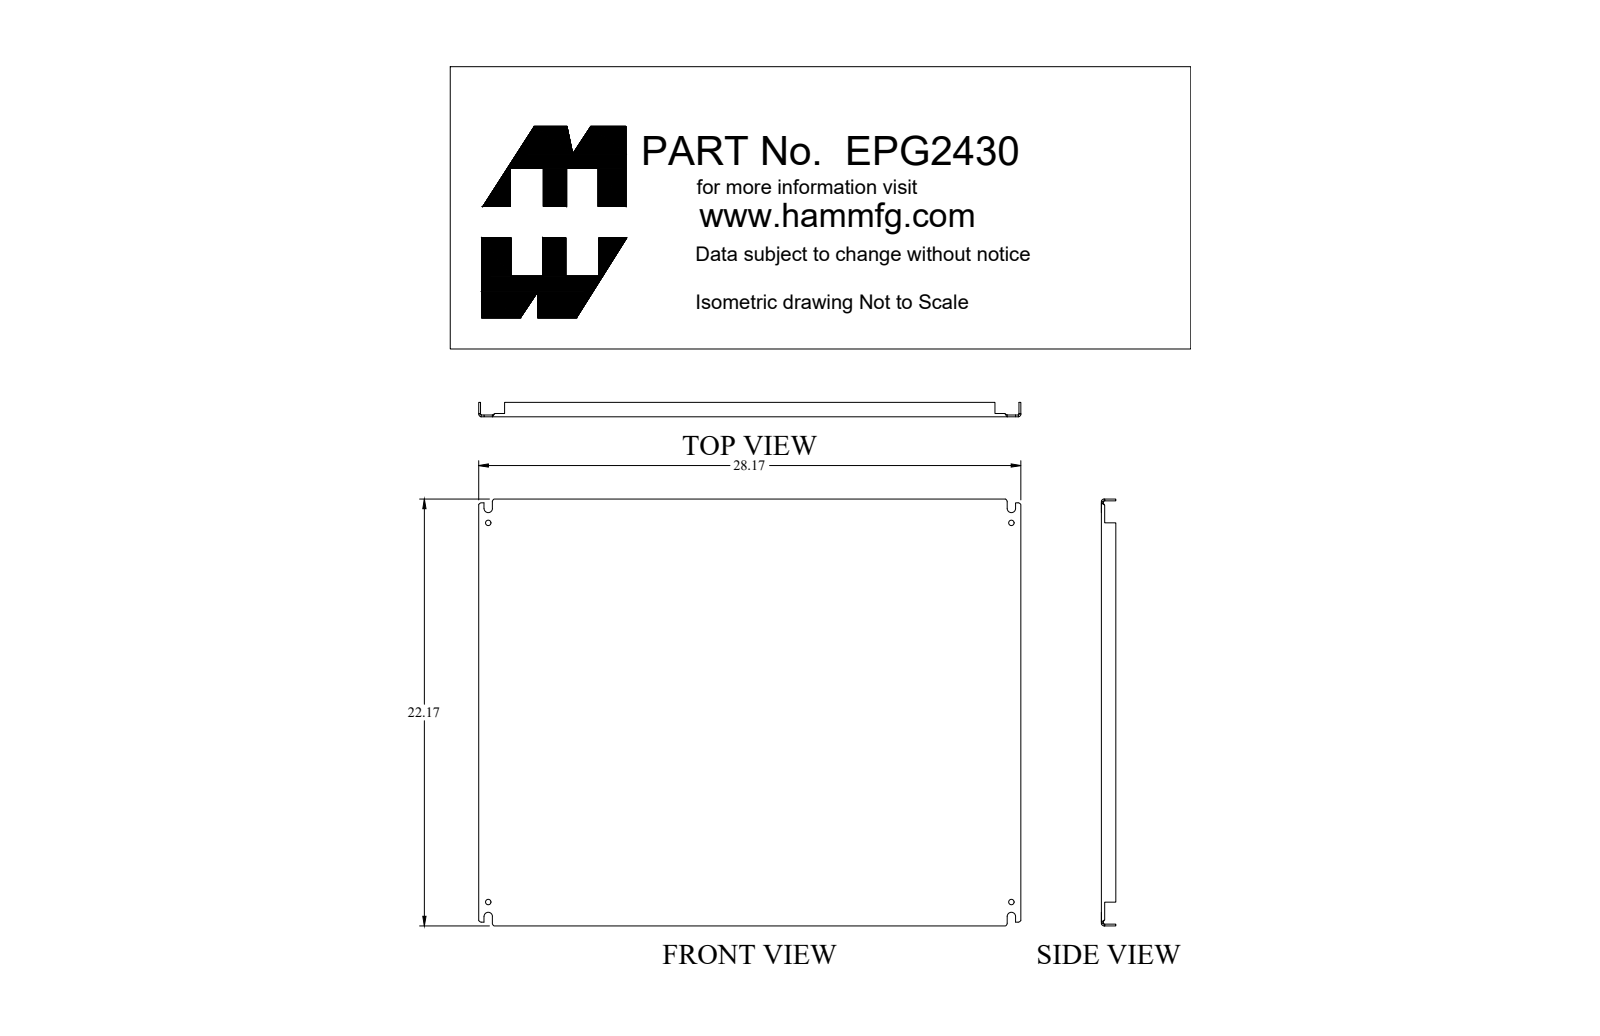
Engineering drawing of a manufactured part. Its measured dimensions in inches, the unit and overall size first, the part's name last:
Units: inches
Overall size (bounding box): 28.17 × 22.17 × 0.75
Round holes (diameter × count): ⌀0.281 ×4
Partial cylindrical surfaces — rounded edges, fillets, slot ends (radius × count): R0.048 ×4, R0.063 ×4, R0.143 ×4, R0.219 ×4
Main face-to-face distances: 0.095, 22.075, 28.075, 21.98, 22.17, 27.98, 28.17, 0.75, 0.655, 0.171
Hole centre spacings: 19.688, 27.188, 33.568
Volume: 64.45 in³ · Surface area: 1 367 in²
Bodies: 1 solid, 128 faces (74 planar, 38 cylindrical, 16 other)
Part name (STEP PRODUCT): EPG2430
STEP written by: SolidWorks 2018 (AUTOMOTIVE_DESIGN)
